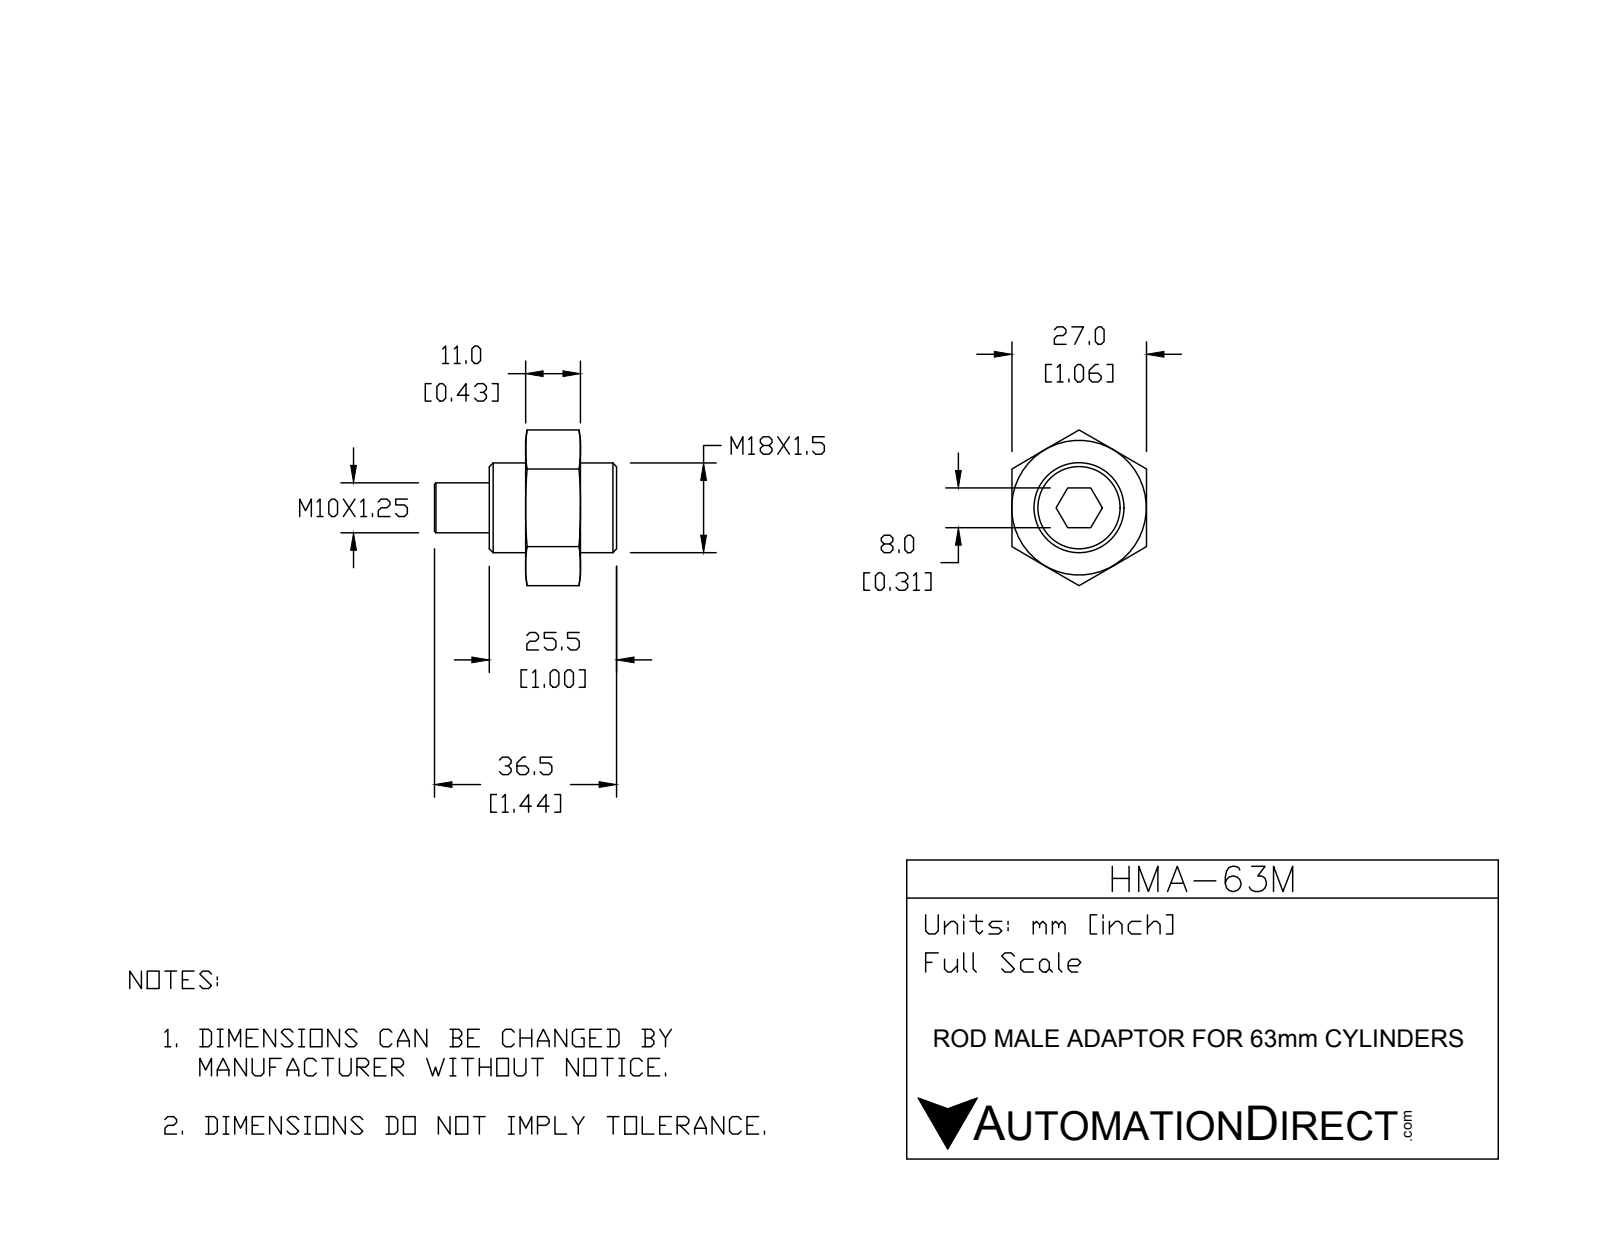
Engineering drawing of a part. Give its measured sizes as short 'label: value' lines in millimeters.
name: HMA-63M
written by: SolidWorks 2015 (CONFIG_CONTROL_DESIGN)
unit: mm
bodies: 2 solids, 44 faces (18 planar, 6 cylindrical, 20 other)
size: 36.5 × 31.18 × 27
volume: 10 955 mm³; area: 4 874 mm²
holes: 1× ⌀18
bosses: 1× ⌀10
face distances: 27, 11, 18.25, 7.25, 25.5, 8, 36.5, 29.25, 9, 1.75
